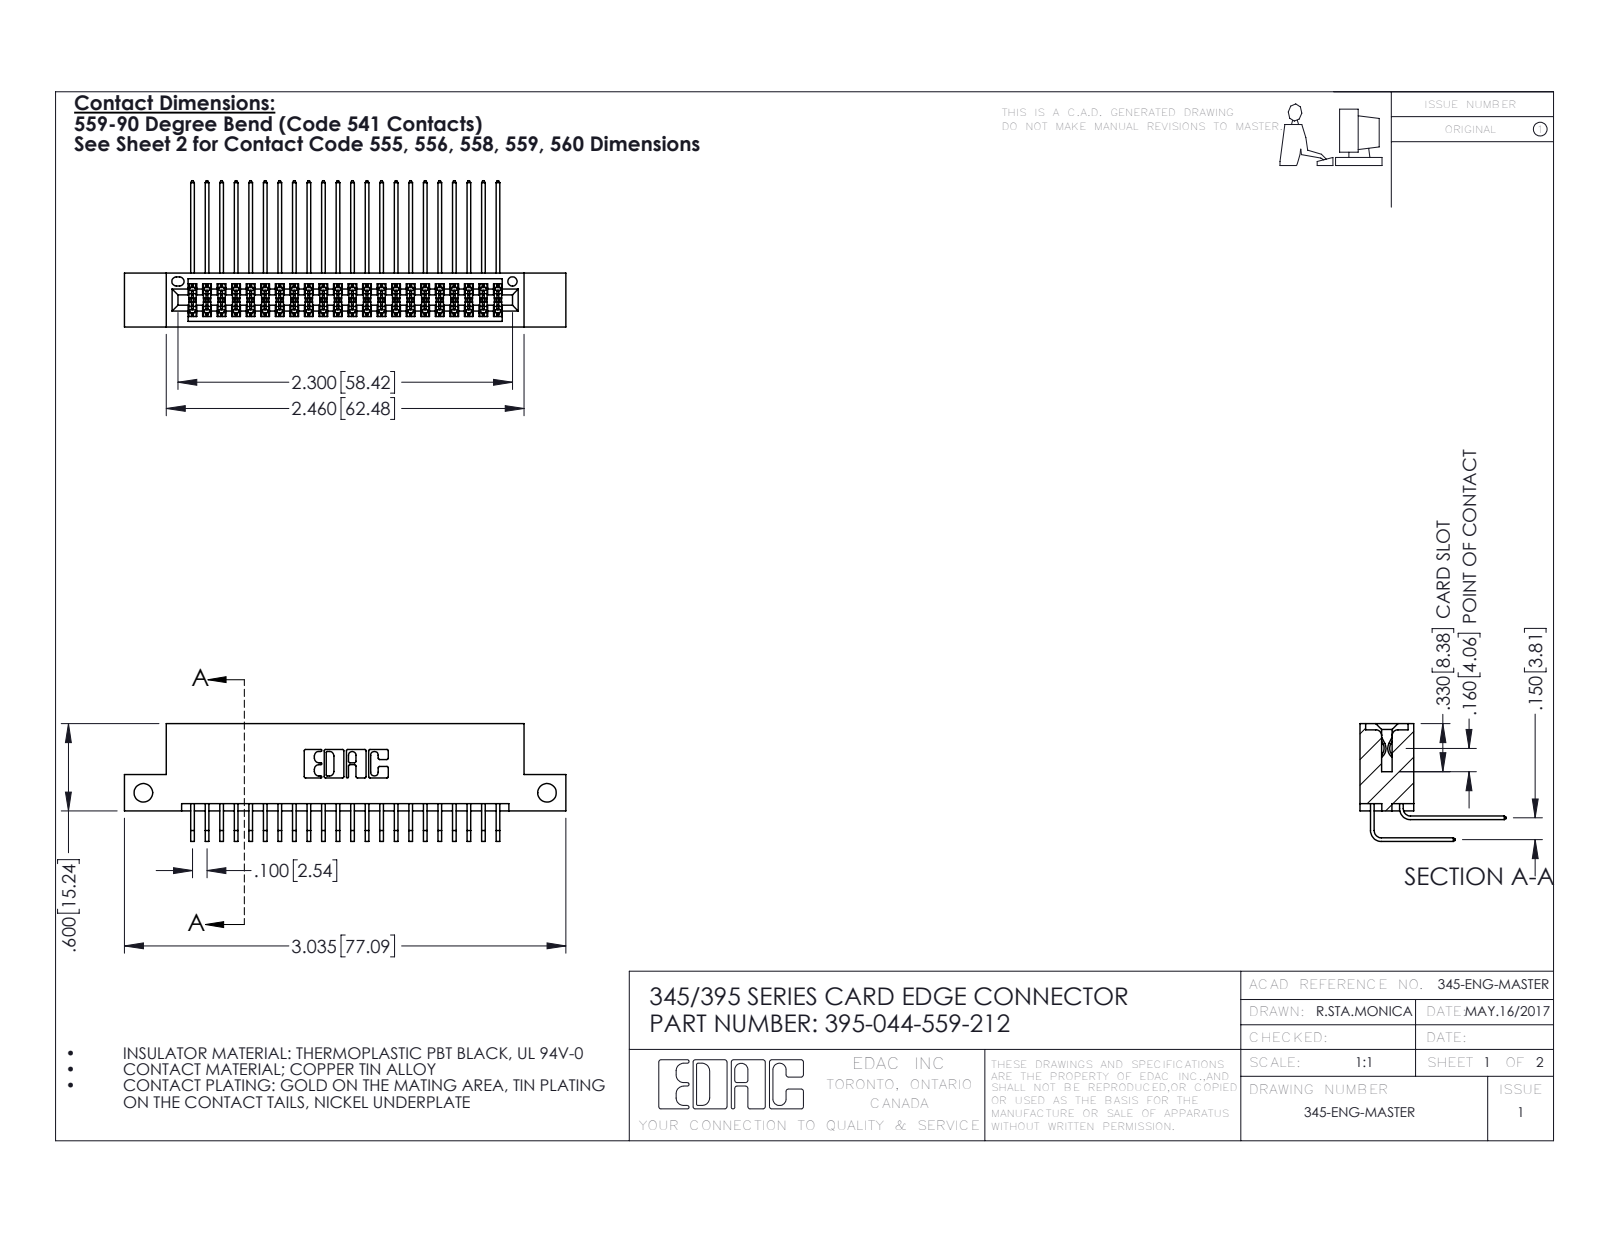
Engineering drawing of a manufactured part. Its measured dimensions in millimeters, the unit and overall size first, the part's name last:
Units: millimetres
Overall size (bounding box): 77.1 × 25.5 × 20.5
Round holes (diameter × count): ⌀3.3 ×2, ⌀1.6 ×1
Partial cylindrical surfaces — rounded edges, fillets, slot ends (radius × count): R0.2 ×67, R0.3 ×22, R0.2 ×6, R0.8 ×6, R0.7 ×3, R0.4 ×2, R0.5 ×2, R0.6 ×2
Main face-to-face distances: 1.8, 7.6, 5.1, 9.4, 2.5, 6.9, 0.6, 5.7, 3.8, 4.4
Hole centre spacings: 70.5
Volume: 7 470 mm³ · Surface area: 11 710 mm²
Bodies: 45 solids, 2414 faces (1620 planar, 794 cylindrical, 0 other)
Part name (STEP PRODUCT): 395-044-559-212; 345 Part_Flush Mounting Lugs - Side Mount; 345-292-001_558 559 Tail - 1; 345-292-001_559 Tail - 2
STEP written by: SolidWorks 2016 (CONFIG_CONTROL_DESIGN)
